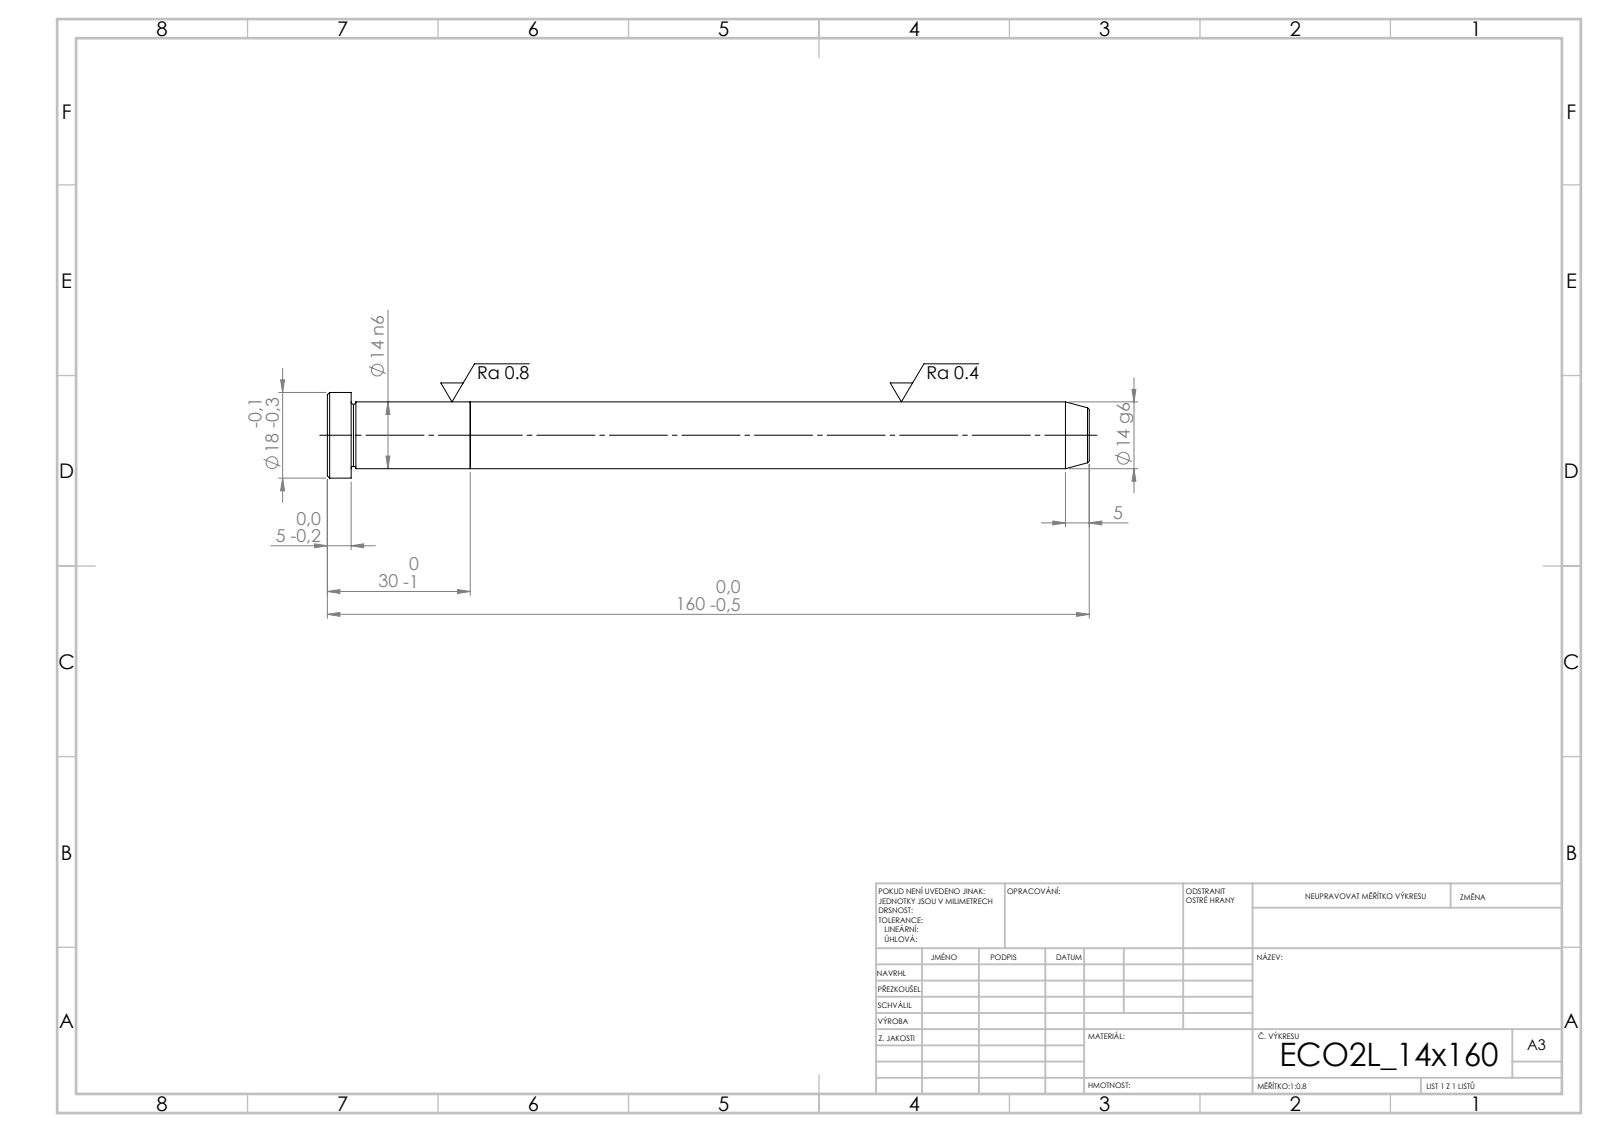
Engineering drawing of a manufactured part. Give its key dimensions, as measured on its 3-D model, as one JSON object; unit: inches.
{"step_written_by": "SolidWorks 2019 (CONFIG_CONTROL_DESIGN)", "units": "inches", "bodies": {"solids": 2, "faces": 21, "planar": 5, "cylindrical": 6, "other": 10}, "overall_size": [6.299, 0.709, 0.709], "volume_in3": 1.524, "surface_area_in2": 12.17, "round_bosses_or_shafts": [[0.709, 1], [0.551, 1]], "face_to_face_distances": [1.181, 0.984, 0.197, 5.118, 6.102, 6.299]}
